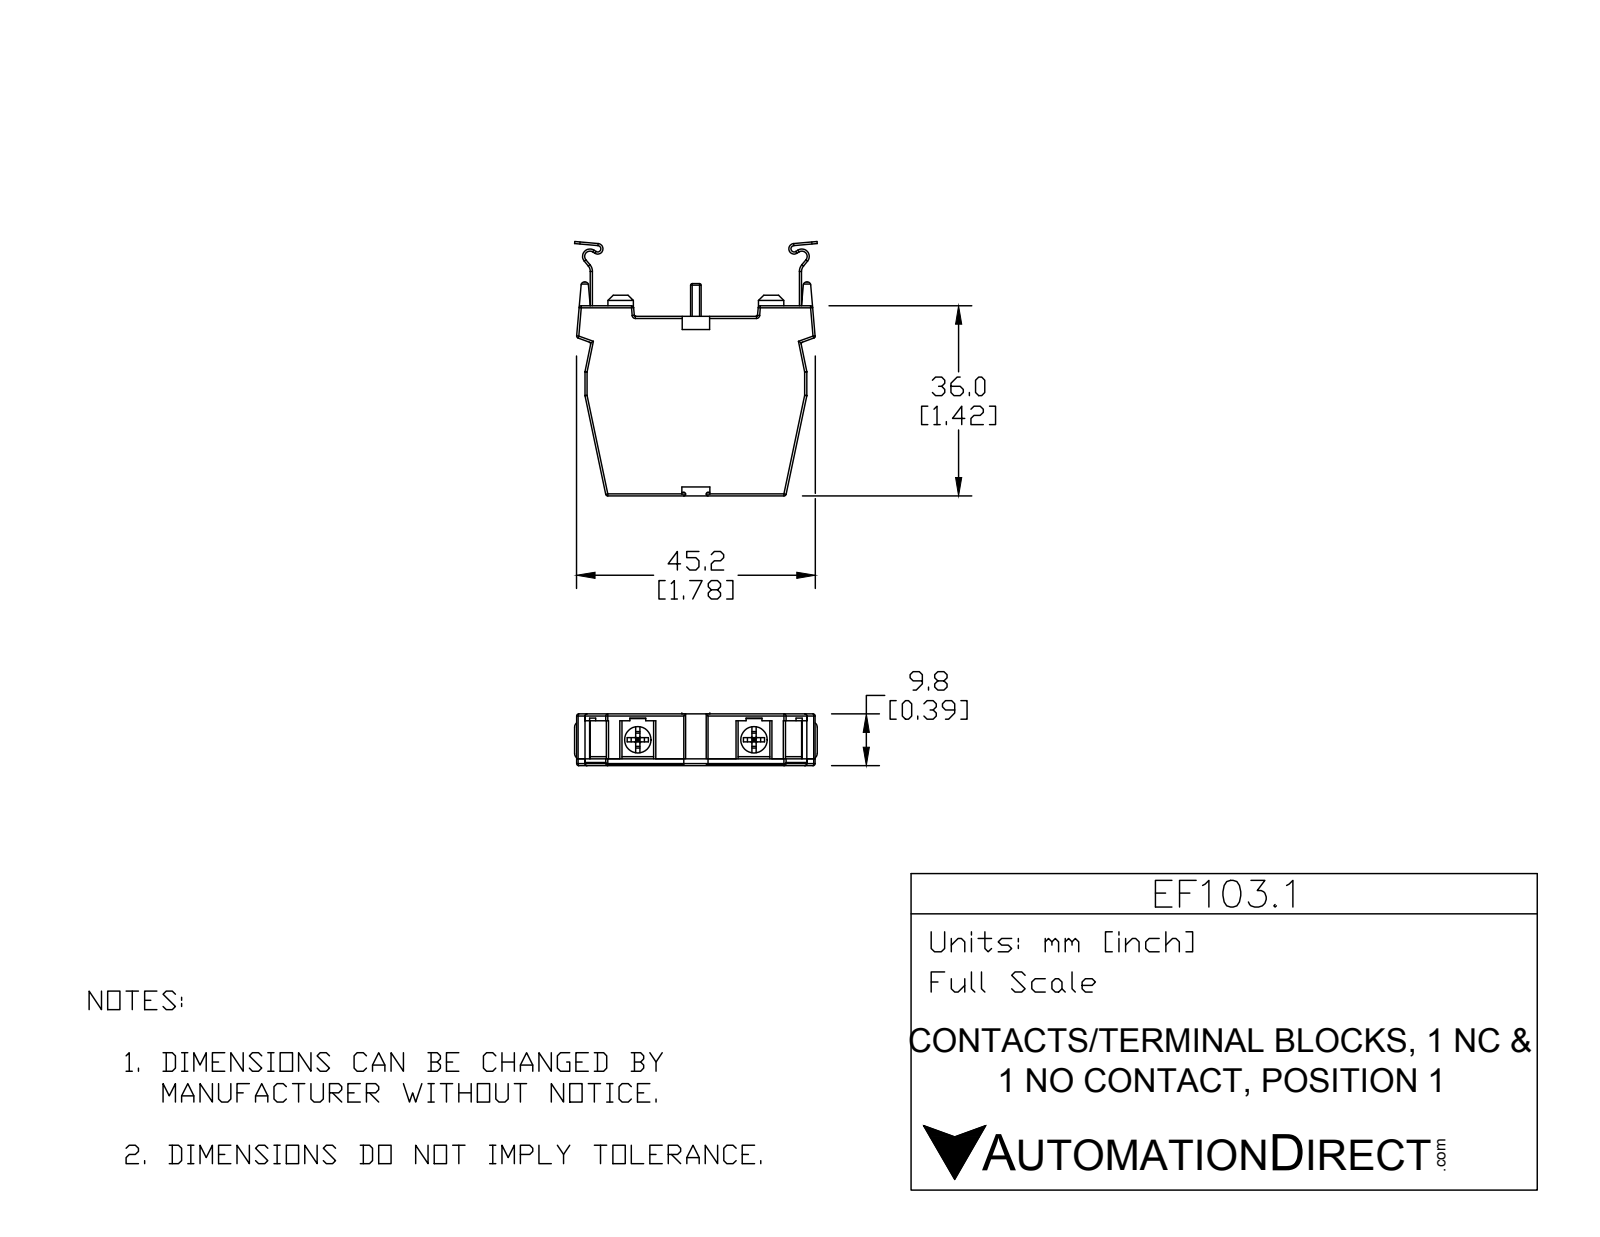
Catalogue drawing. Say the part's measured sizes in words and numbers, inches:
The part is named "EF103.1". Its 3-D file was written by "SolidWorks 2015 (AUTOMOTIVE_DESIGN)". It is 7 solids with 299 faces: 173 planar, 104 cylindrical and 22 other. Overall it measures 1.896 by 1.822 by 0.386 inches. Its volume is 0.741 cubic inches and its surface area 10.24 square inches. Round holes: 4 of diameter 0.197. Round bosses or shafts: 4 of diameter 0.157, 2 of diameter 0.187. Partial cylindrical surfaces (rounded edges, fillets, slot ends): 44 of radius 0.01, 8 of radius 0.02, 6 of radius 0.039, 4 of radius 0.024, 2 of radius 0.024, 2 of radius 0.039, 2 of radius 0.055, 2 of radius 0.063. The main face-to-face distances are 0.386, 0.055, 0.331, 1.339, 0.276, 0.079, 0.016, 0.125, 1.464, 1.417. The hole center spacings are 0.859.
